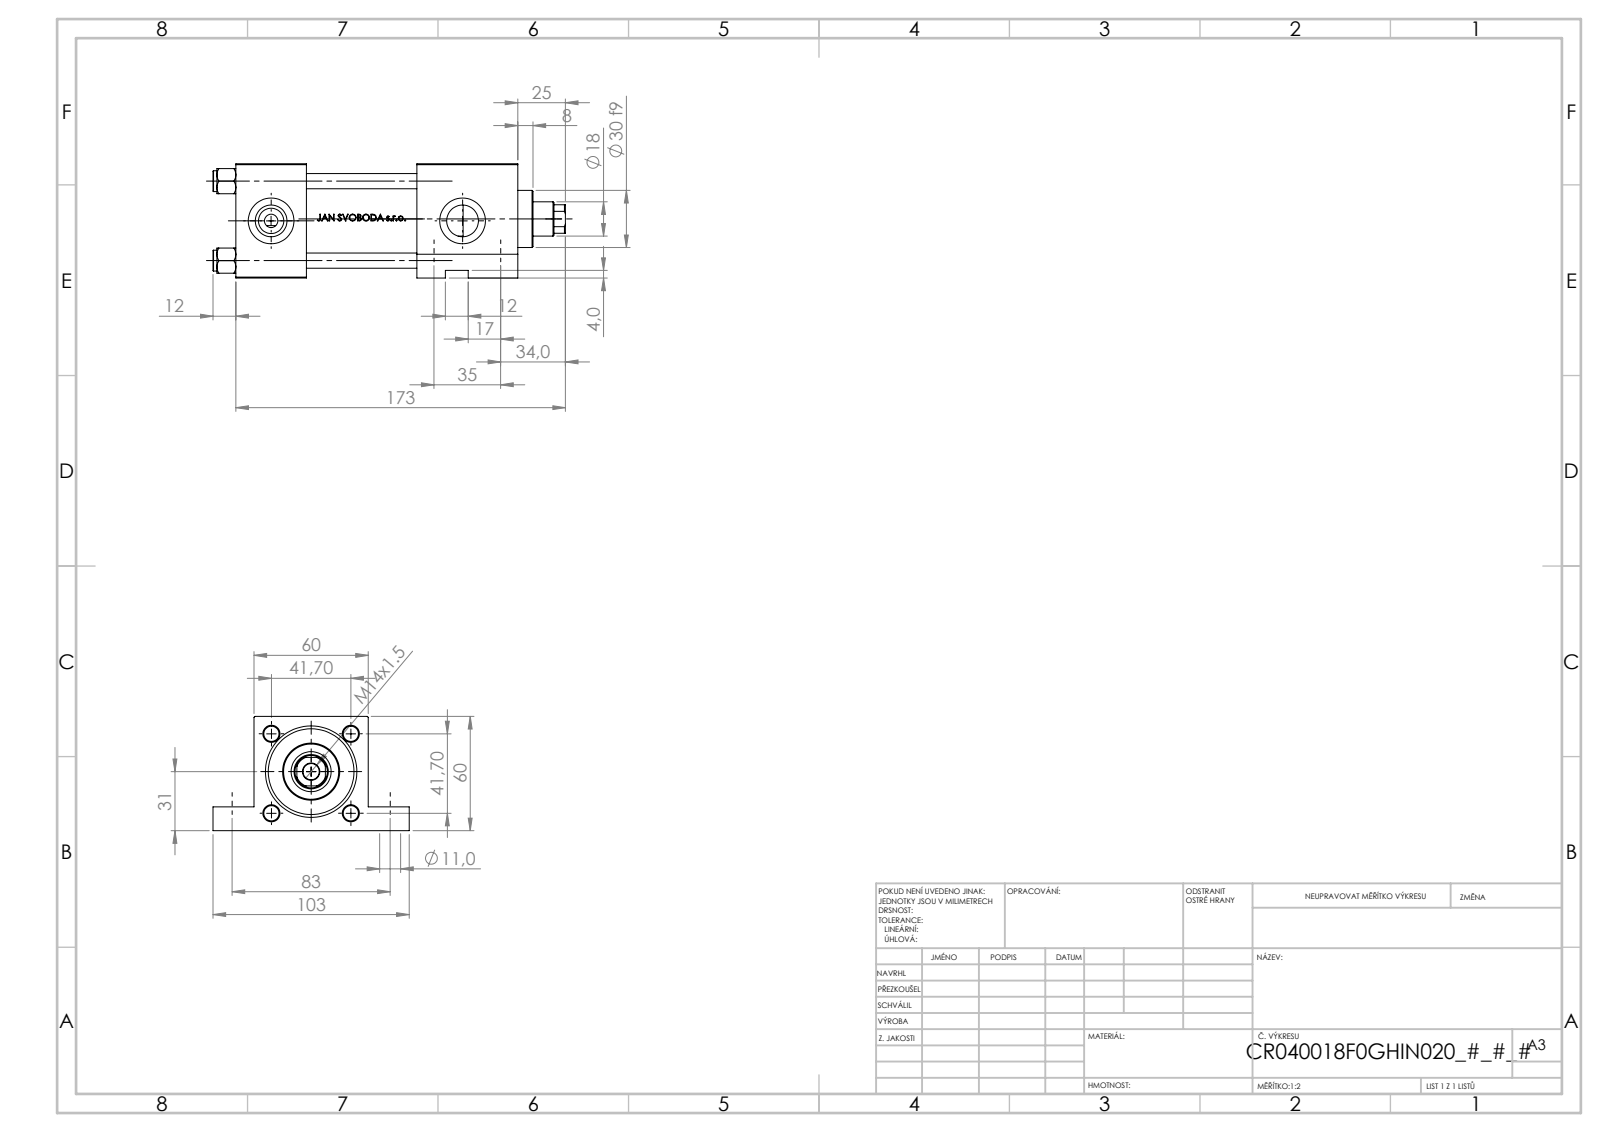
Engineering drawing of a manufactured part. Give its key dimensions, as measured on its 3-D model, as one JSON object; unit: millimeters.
{"part_name": "NUT_M5_F; V215CR_VCP_F; V215CR_F_Body; V215_VC_A (+1 more)", "step_written_by": "SolidWorks 2019 (CONFIG_CONTROL_DESIGN)", "units": "millimeters", "bodies": {"solids": 11, "faces": 1118, "planar": 437, "cylindrical": 141, "other": 540}, "overall_size": [185, 103, 60], "volume_mm3": 423631, "surface_area_mm2": 111537, "round_holes": [[8, 4], [7, 2], [11, 2], [11, 2], [16.66, 2], [24, 2], [8.5, 1], [18, 1], [21, 1], [31, 1], [40, 1], [45, 1]], "round_bosses_or_shafts": [[11, 4], [46, 1], [30, 1]], "partial_cylinders_radius": [[8.5, 1]], "face_to_face_distances": [60, 37, 148, 111, 95, 58, 53, 119.3, 82.3, 24.3], "hole_center_spacings": [41.7, 28.79, 30.2, 35, 58.97, 83, 90.08, 100.5]}
